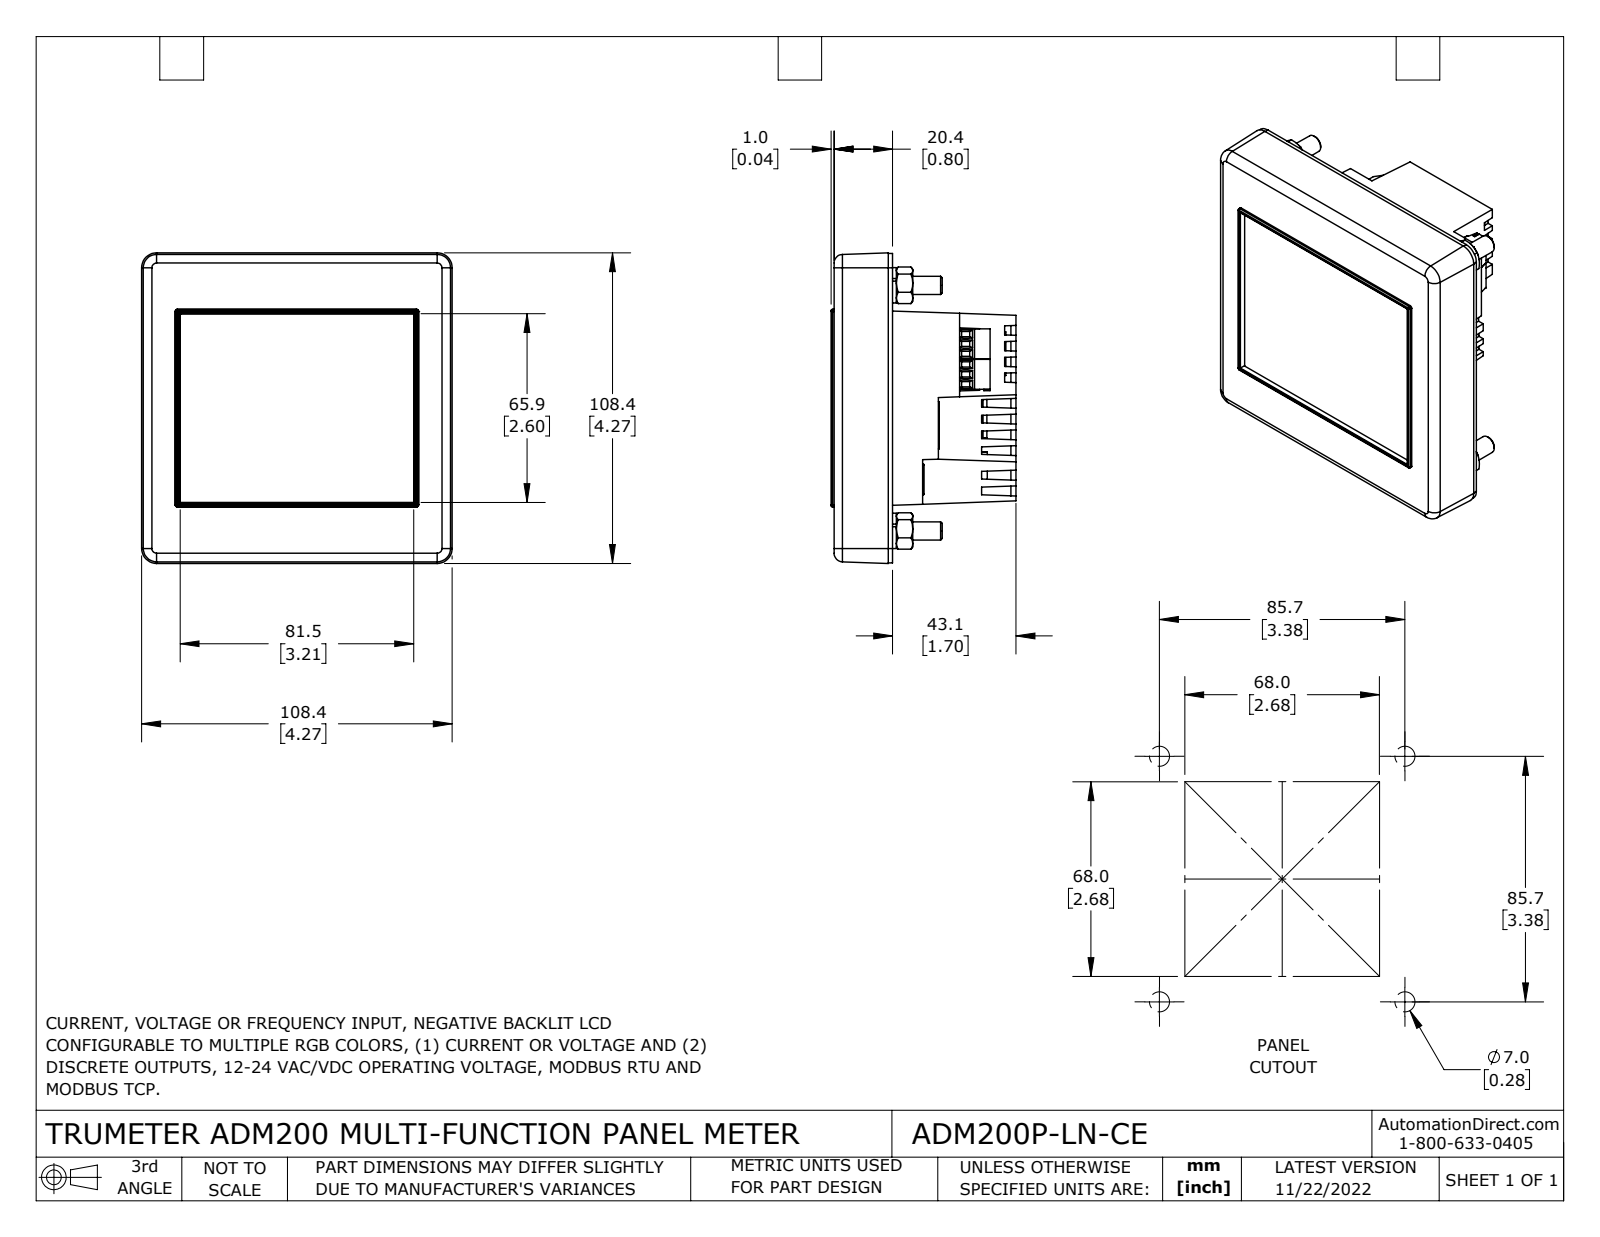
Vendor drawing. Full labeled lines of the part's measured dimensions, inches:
Part name (STEP PRODUCT): ADM200P-LN-CE
STEP written by: SolidWorks 2021 (CONFIG_CONTROL_DESIGN)
Units: inches
Bodies: 23 solids, 2059 faces (1384 planar, 290 cylindrical, 385 other)
Overall size (bounding box): 4.269 × 4.269 × 2.541
Volume: 7.808 in³ · Surface area: 190.8 in²
Round holes (diameter × count): ⌀0.071 ×9, ⌀0.114 ×6, ⌀0.118 ×5, ⌀0.213 ×4, ⌀0.25 ×4, ⌀0.26 ×4, ⌀0.295 ×4, ⌀0.154 ×2
Round bosses / shafts (diameter × count): ⌀0.039 ×5, ⌀0.487 ×4, ⌀0.438 ×4, ⌀0.024 ×4, ⌀0.079 ×2
Partial cylindrical surfaces — rounded edges, fillets, slot ends (radius × count): R0.006 ×32, R0.02 ×30, R0.039 ×7, R0.016 ×4, R0.03 ×4, R0.118 ×4, R0.197 ×4, R0.004 ×2
Main face-to-face distances: 0.031, 0.635, 0.11, 0.073, 0.059, 0.079, 0.694, 3.395, 3.468, 0.047
Hole centre spacings: 0.709, 3.228, 0.136, 0.293, 0.986, 1.417, 2.126, 2.399
